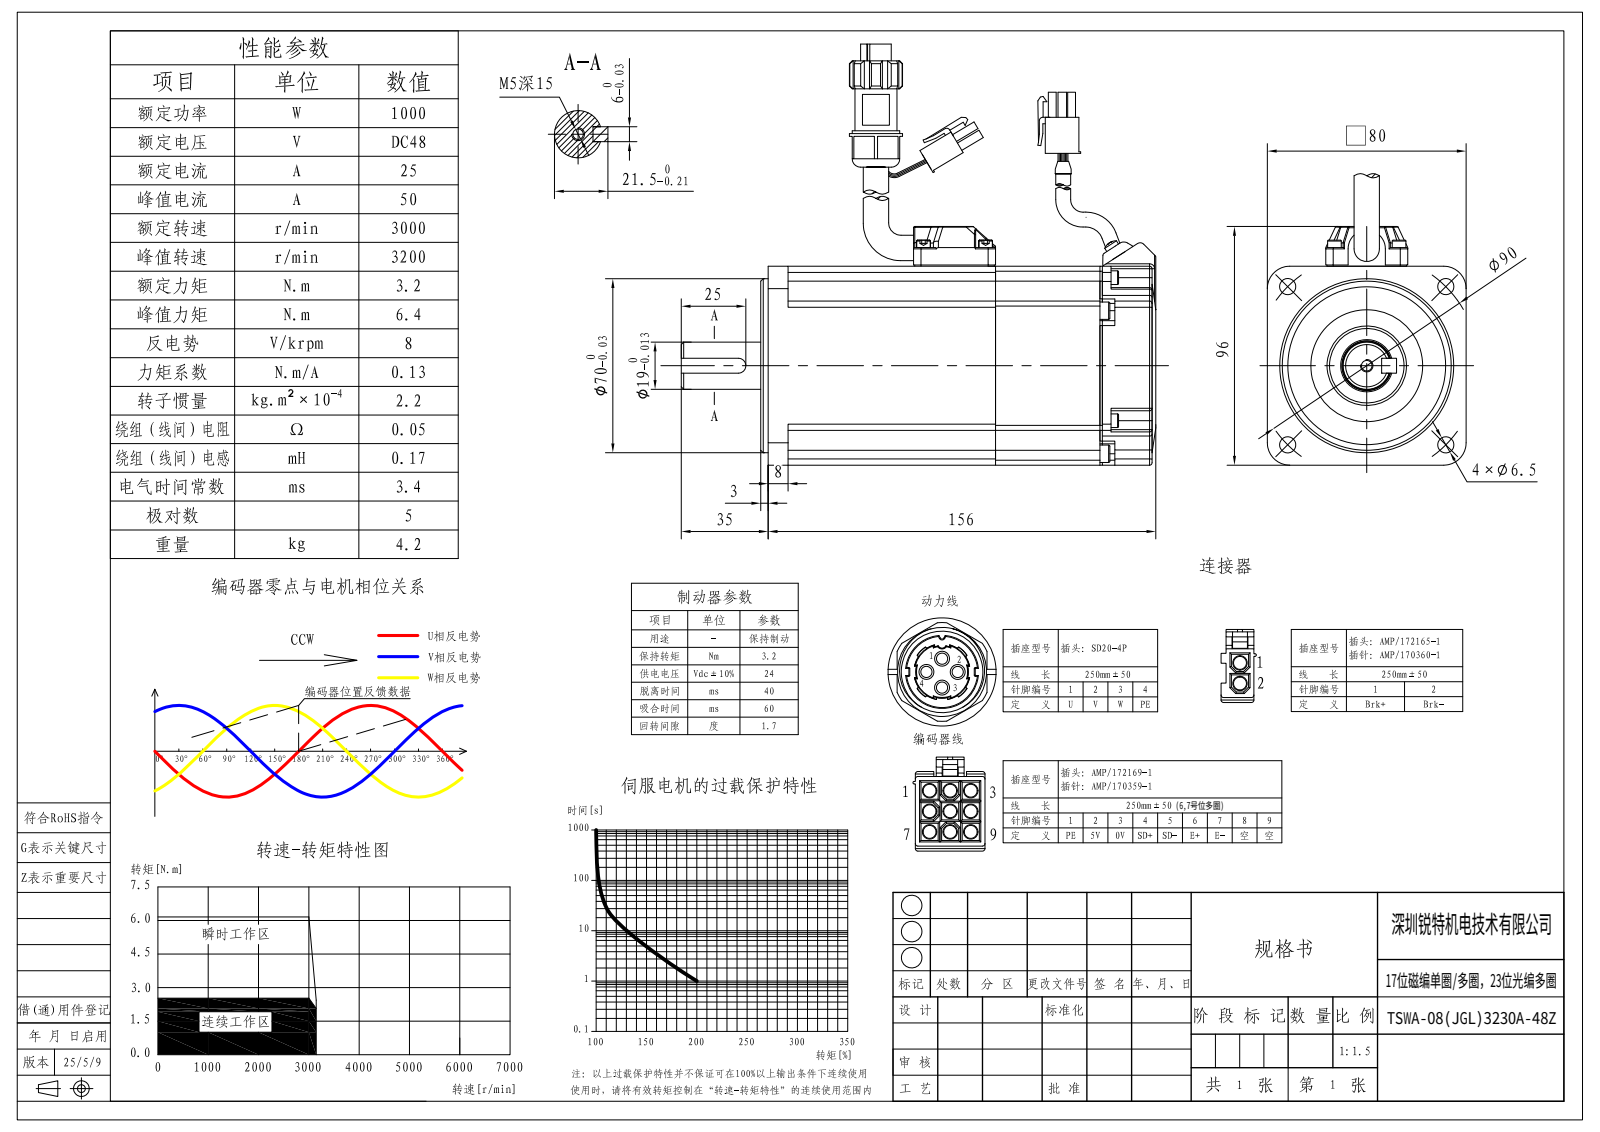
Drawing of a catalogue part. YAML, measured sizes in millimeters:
step_written_by: "SolidWorks 2018 (CONFIG_CONTROL_DESIGN)"
units: millimeters
bodies: {solids: 13, faces: 1230, planar: 476, cylindrical: 435, other: 319}
overall_size: [194.5, 92.5, 80]
volume: 909332
surface_area: 105543
round_holes:
  - {diameter: 3.3, count: 14}
  - {diameter: 3.2, count: 8}
  - {diameter: 4.2, count: 5}
  - {diameter: 3.5, count: 4}
  - {diameter: 4.5, count: 4}
  - {diameter: 6.5, count: 4}
  - {diameter: 2.5, count: 3}
  - {diameter: 2, count: 2}
  - {diameter: 6, count: 1}
  - {diameter: 6.3, count: 1}
  - {diameter: 7.6, count: 1}
  - {diameter: 8, count: 1}
round_bosses_or_shafts:
  - {diameter: 4, count: 10}
  - {diameter: 7, count: 8}
  - {diameter: 5.5, count: 6}
  - {diameter: 3, count: 6}
  - {diameter: 2.2, count: 2}
  - {diameter: 2, count: 2}
  - {diameter: 70, count: 1}
  - {diameter: 62, count: 1}
partial_cylinders:
  - {radius: 1, count: 49}
  - {radius: 0.5, count: 25}
  - {radius: 2, count: 21}
  - {radius: 8, count: 12}
  - {radius: 0.6, count: 9}
  - {radius: 2.5, count: 8}
  - {radius: 4, count: 8}
  - {radius: 3, count: 5}
face_to_face_distances: [80, 14, 66, 61, 1, 3.5, 159.5, 3, 2.5, 0.5]
hole_center_spacings: [10.34, 10.39, 18.73, 41.5, 41.75, 43.98, 44.11, 53.92]
